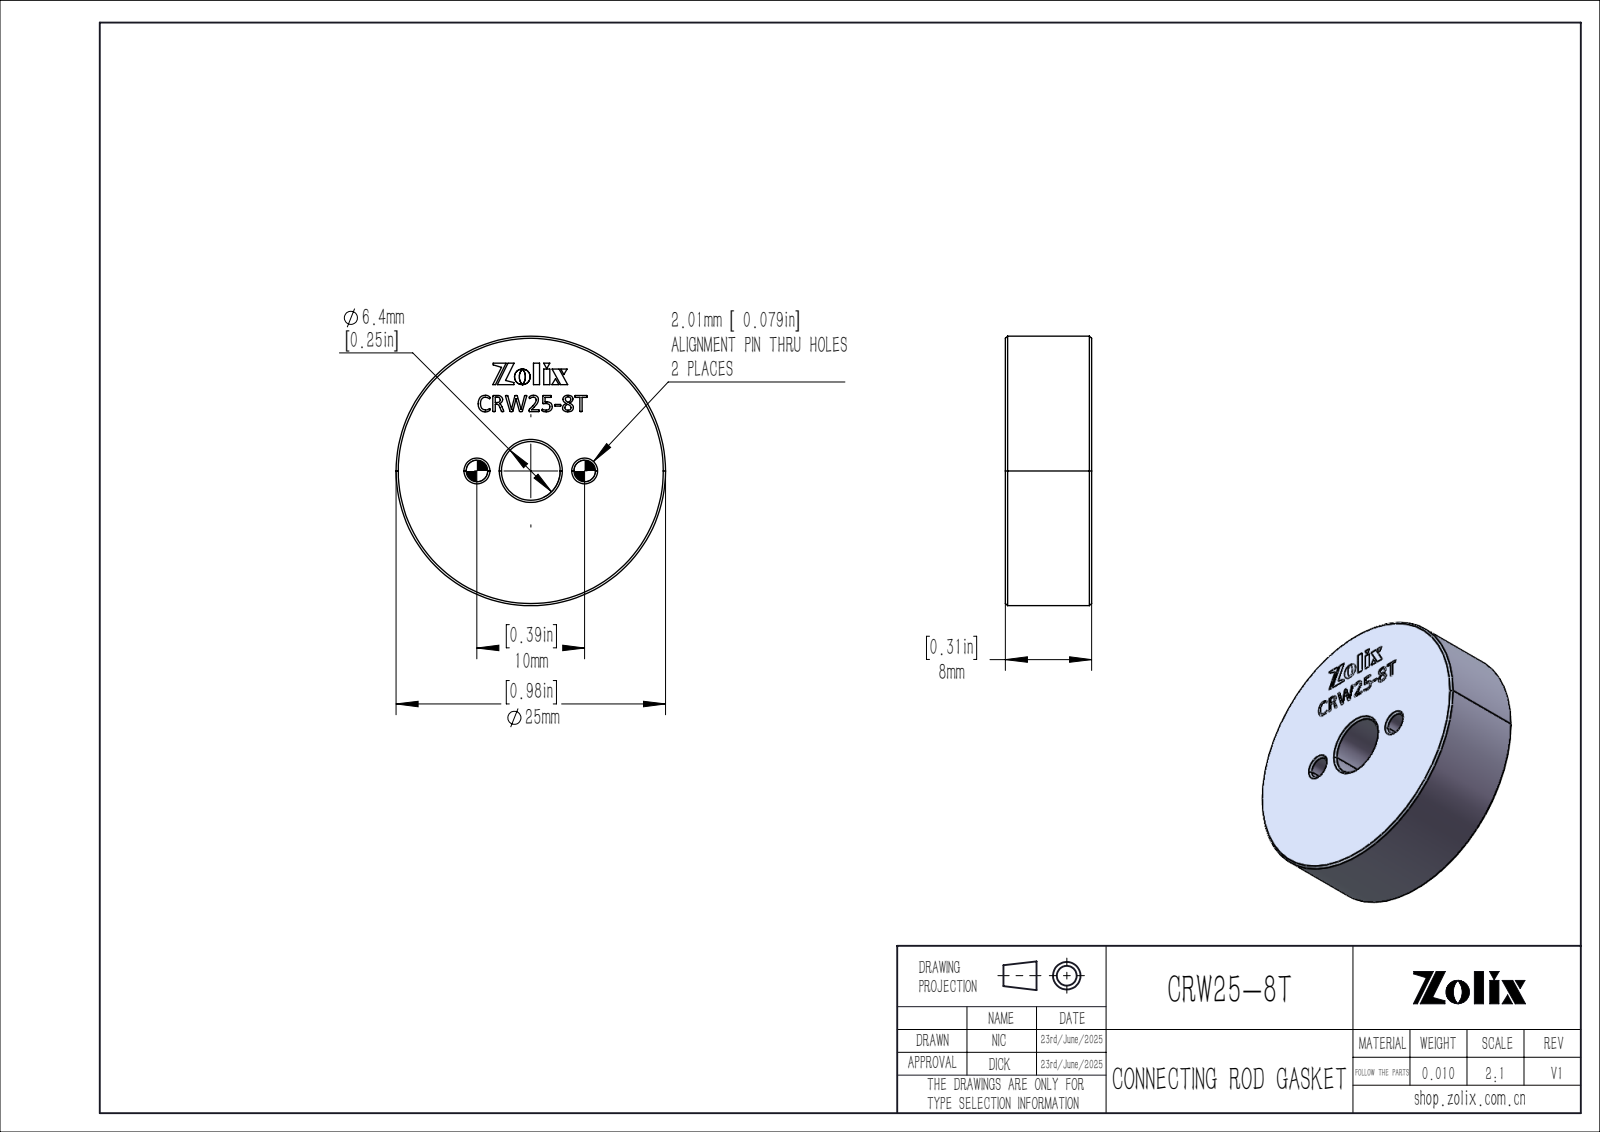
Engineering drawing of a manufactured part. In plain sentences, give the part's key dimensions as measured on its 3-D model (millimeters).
The part is named "CRW25-8T". Its 3-D file was written by "SolidWorks 2020 (CONFIG_CONTROL_DESIGN)". It is 1 solid with 329 faces: 221 planar, 8 cylindrical and 100 other. Overall it measures 25 by 25 by 8 millimeters. Its volume is 3 686 cubic millimeters and its surface area 1 765 square millimeters. Round holes: 2 of diameter 2, 1 of diameter 5.45. Round bosses or shafts: 1 of diameter 25. The main face-to-face distances are 8, 7.98, 0.56, 3, 2, 8.07, 1, 4.5, 0.66, 1.44. The hole center spacings are 5, 10.
